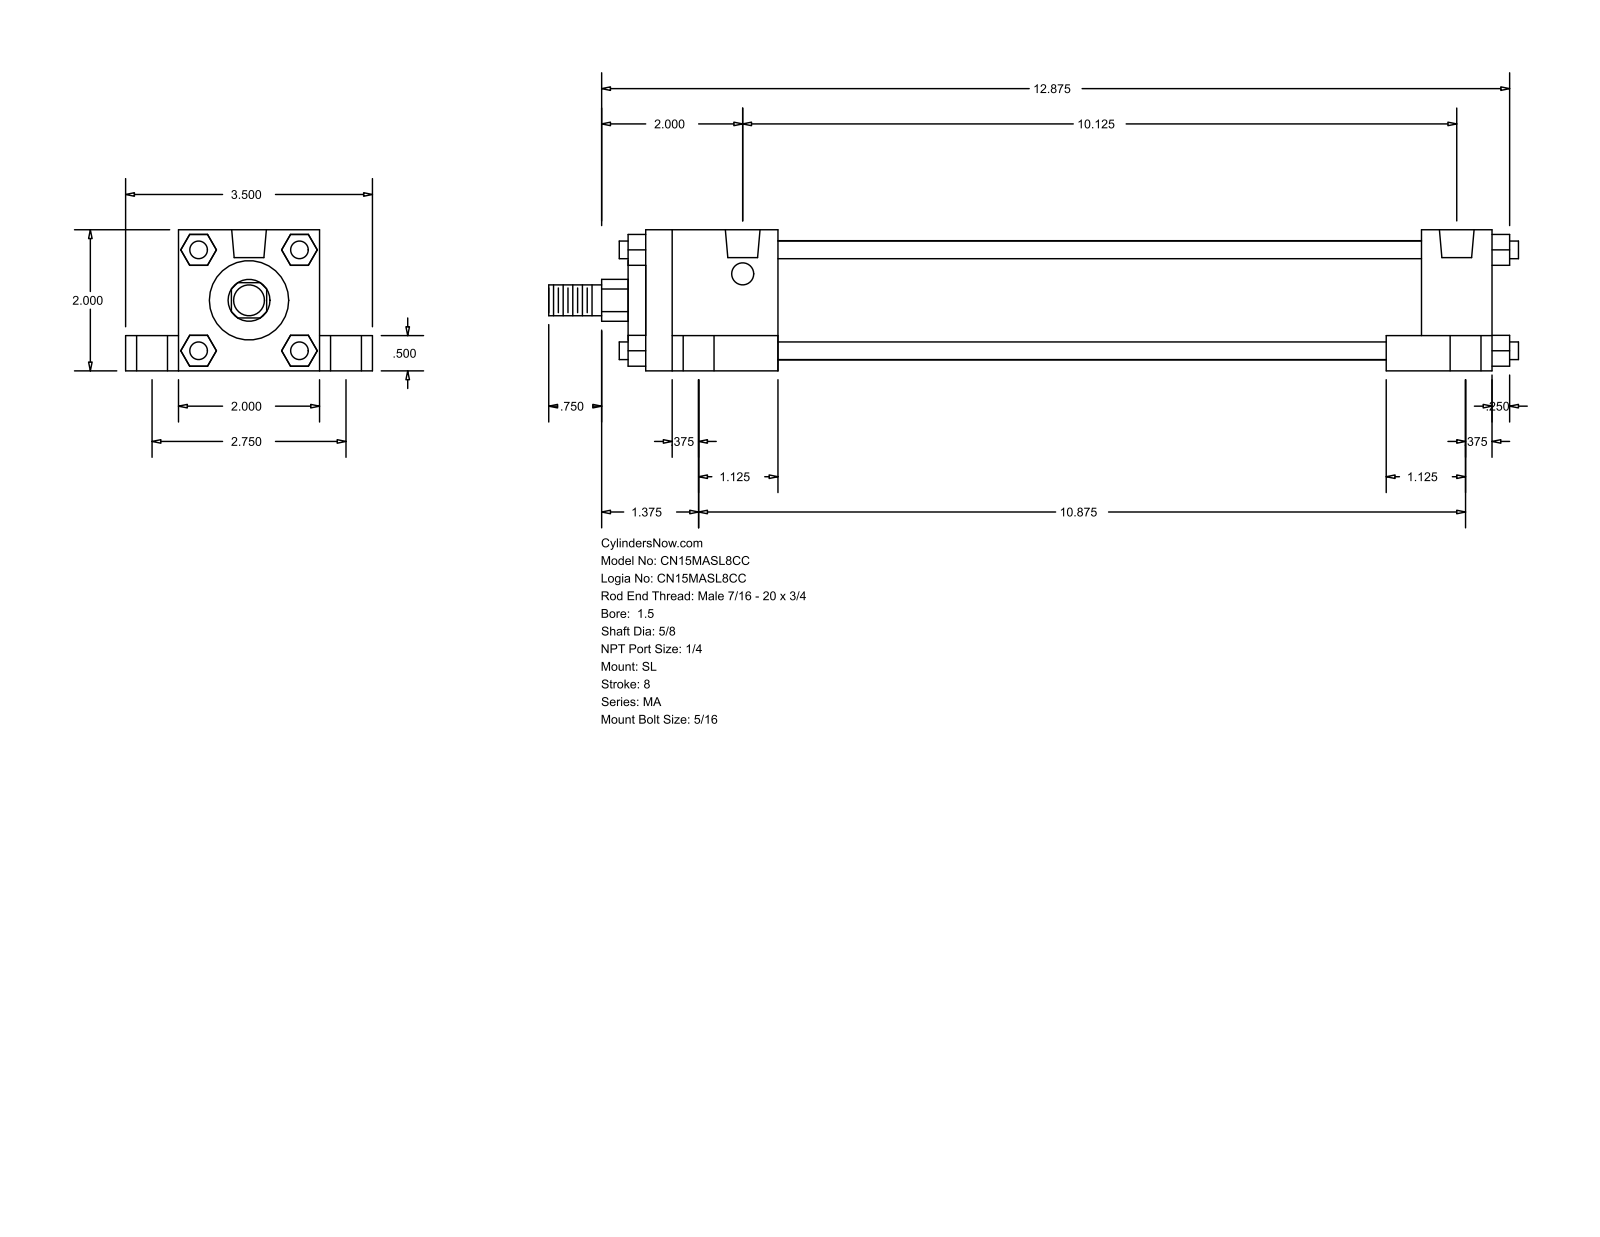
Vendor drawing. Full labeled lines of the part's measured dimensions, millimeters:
Part name (STEP PRODUCT): MA_SL__0150_0.625
STEP written by: GSSL Pune (CONFIG_CONTROL_DESIGN)
Units: millimetres
Bodies: 0 solids, 148 faces (112 planar, 36 cylindrical, 0 other)
Overall size (bounding box): 349.25 × 88.9 × 50.8
Round holes (diameter × count): ⌀7.94 ×4, ⌀11.11 ×4, ⌀17.46 ×4, ⌀12.49 ×2
Round bosses / shafts (diameter × count): ⌀6.35 ×4, ⌀42.93 ×1, ⌀28.57 ×1, ⌀15.88 ×1, ⌀11.11 ×1
Partial cylindrical surfaces — rounded edges, fillets, slot ends (radius × count): R7.54 ×1
Main face-to-face distances: 50.8, 19.05, 38.1, 304.8, 69.85, 12.7, 231.77, 9.52, 279.39, 25.41
Hole centre spacings: 35.06, 38.36, 69.84, 257.18, 262.68, 275.28, 276.23, 284.92
